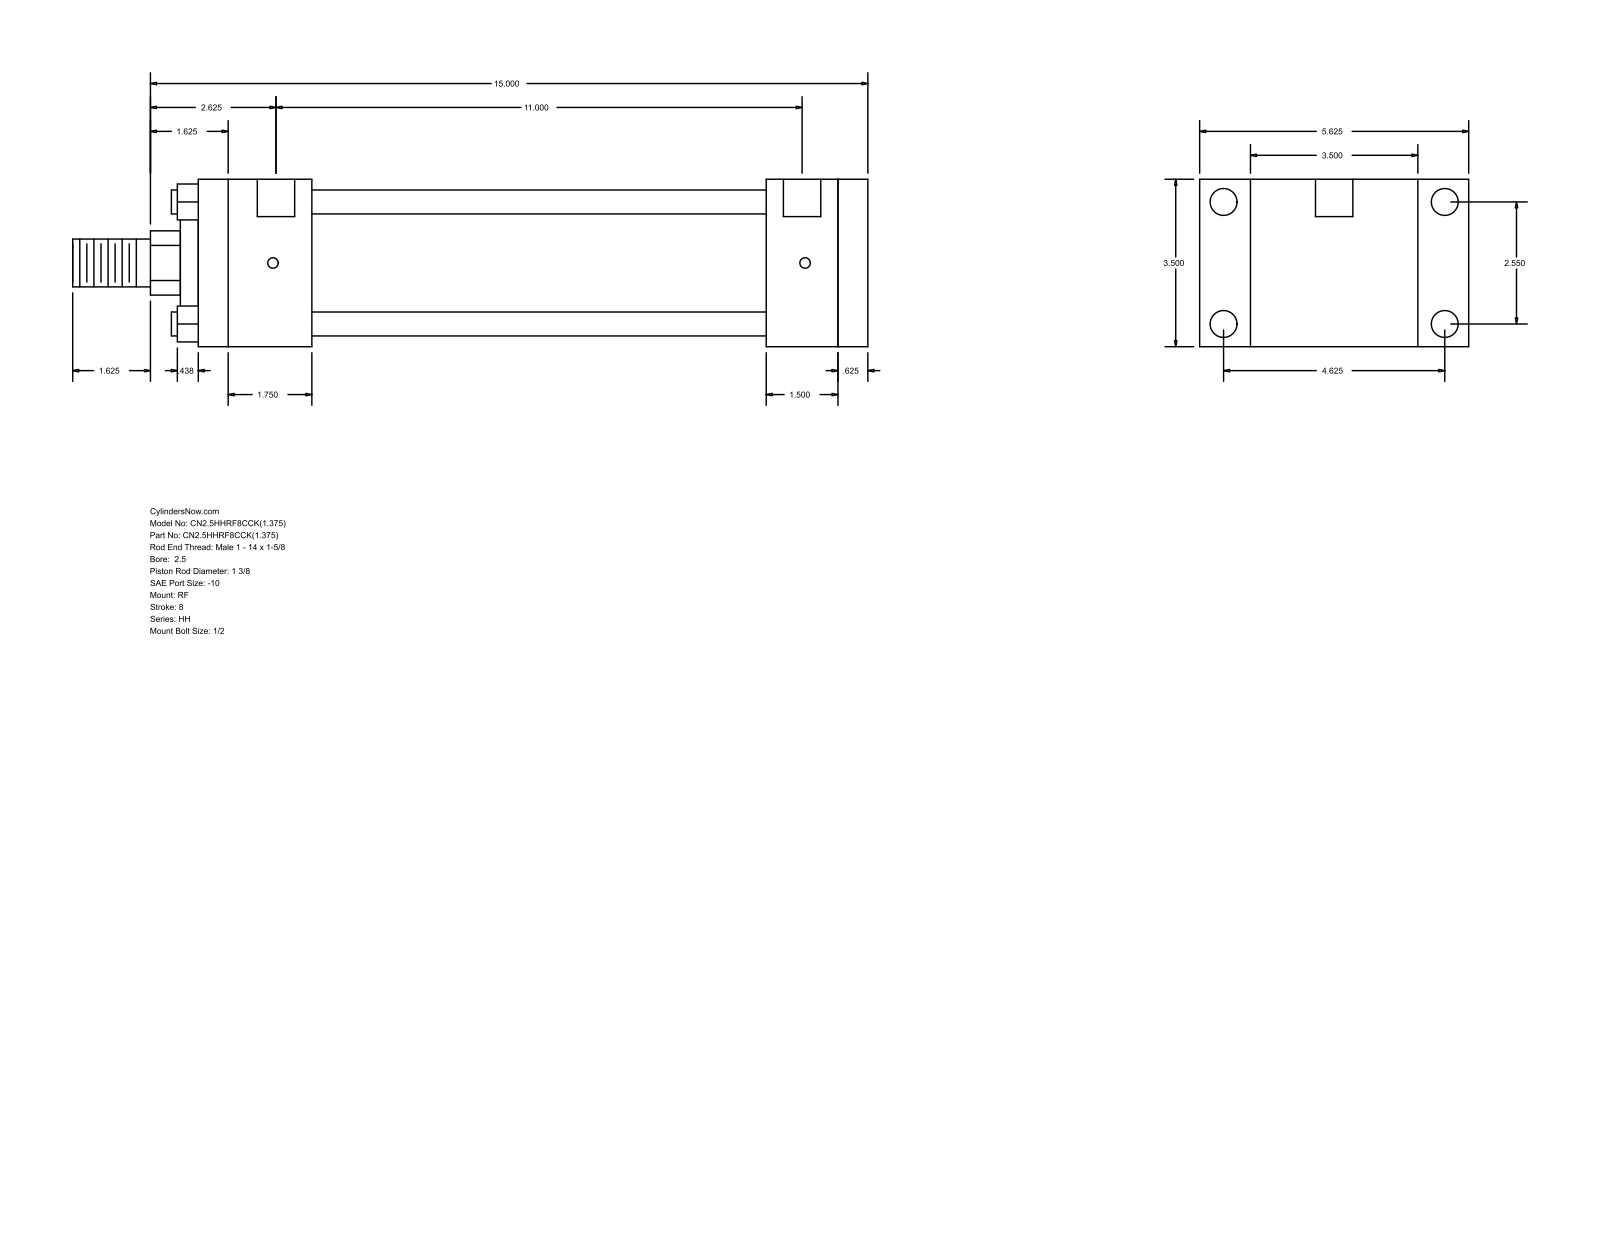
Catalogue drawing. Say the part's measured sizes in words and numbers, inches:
The part is named "HH_RF__0250_1.375". Its 3-D file was written by "GSSL Pune (CONFIG_CONTROL_DESIGN)". It is 0 solids with 92 faces: 64 planar, 28 cylindrical and 0 other. Overall it measures 16.625 by 5.625 by 3.5 inches. Round holes: 4 of diameter 0.219, 4 of diameter 0.563, 2 of diameter 0.781. Round bosses or shafts: 4 of diameter 0.5, 1 of diameter 2.875, 1 of diameter 2, 1 of diameter 1.375, 1 of diameter 1. Partial cylindrical surfaces (rounded edges, fillets, slot ends): 1 of radius 0.672. The main face-to-face distances are 3.5, 14, 0.625, 13.375, 2.375, 11, 11.625, 11.875, 9.5, 1.5. The hole center spacings are 2.55, 4.625, 5.281, 11.125, 0.062, 0.063, 11, 11.062.
